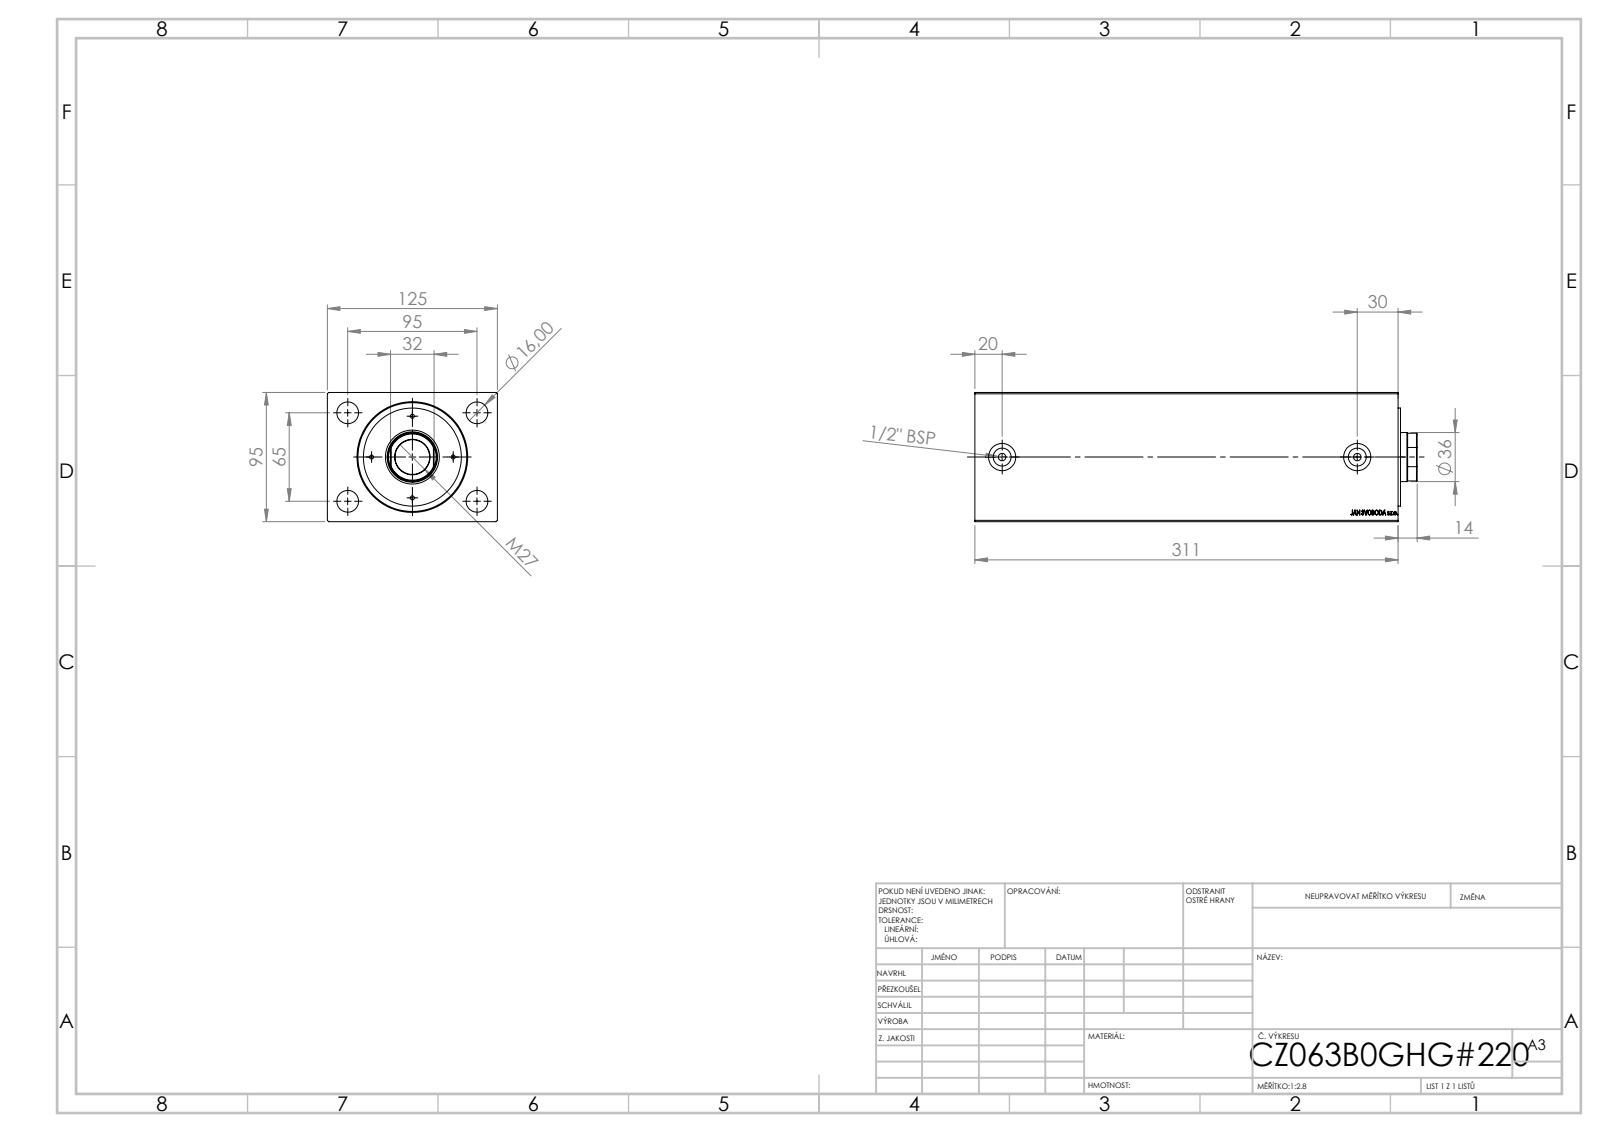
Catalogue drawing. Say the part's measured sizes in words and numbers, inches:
The part is named "V500CZ; V500CZ_B_VC". Its 3-D file was written by "SolidWorks 2019 (CONFIG_CONTROL_DESIGN)". It is 3 solids with 874 faces: 400 planar, 58 cylindrical and 416 other. Overall it measures 12.795 by 4.921 by 3.74 inches. Its volume is 193.6 cubic inches and its surface area 451.7 square inches. Round holes: 4 of diameter 0.118, 4 of diameter 0.63, 2 of diameter 0.217, 2 of diameter 0.518, 2 of diameter 0.787, 1 of diameter 1.004, 1 of diameter 1.417, 1 of diameter 1.457, 1 of diameter 2.48, 1 of diameter 3.15. Round bosses or shafts: 1 of diameter 2.835. Partial cylindrical surfaces (rounded edges, fillets, slot ends): 1 of radius 0.689. The main face-to-face distances are 3.74, 4.921, 12.244, 11.425, 0.819, 0.551, 0.071, 0.48, 10.945, 11.764. The hole center spacings are 1.181, 1.453, 1.67, 1.873, 2.266, 3.091, 3.309, 2.362.
